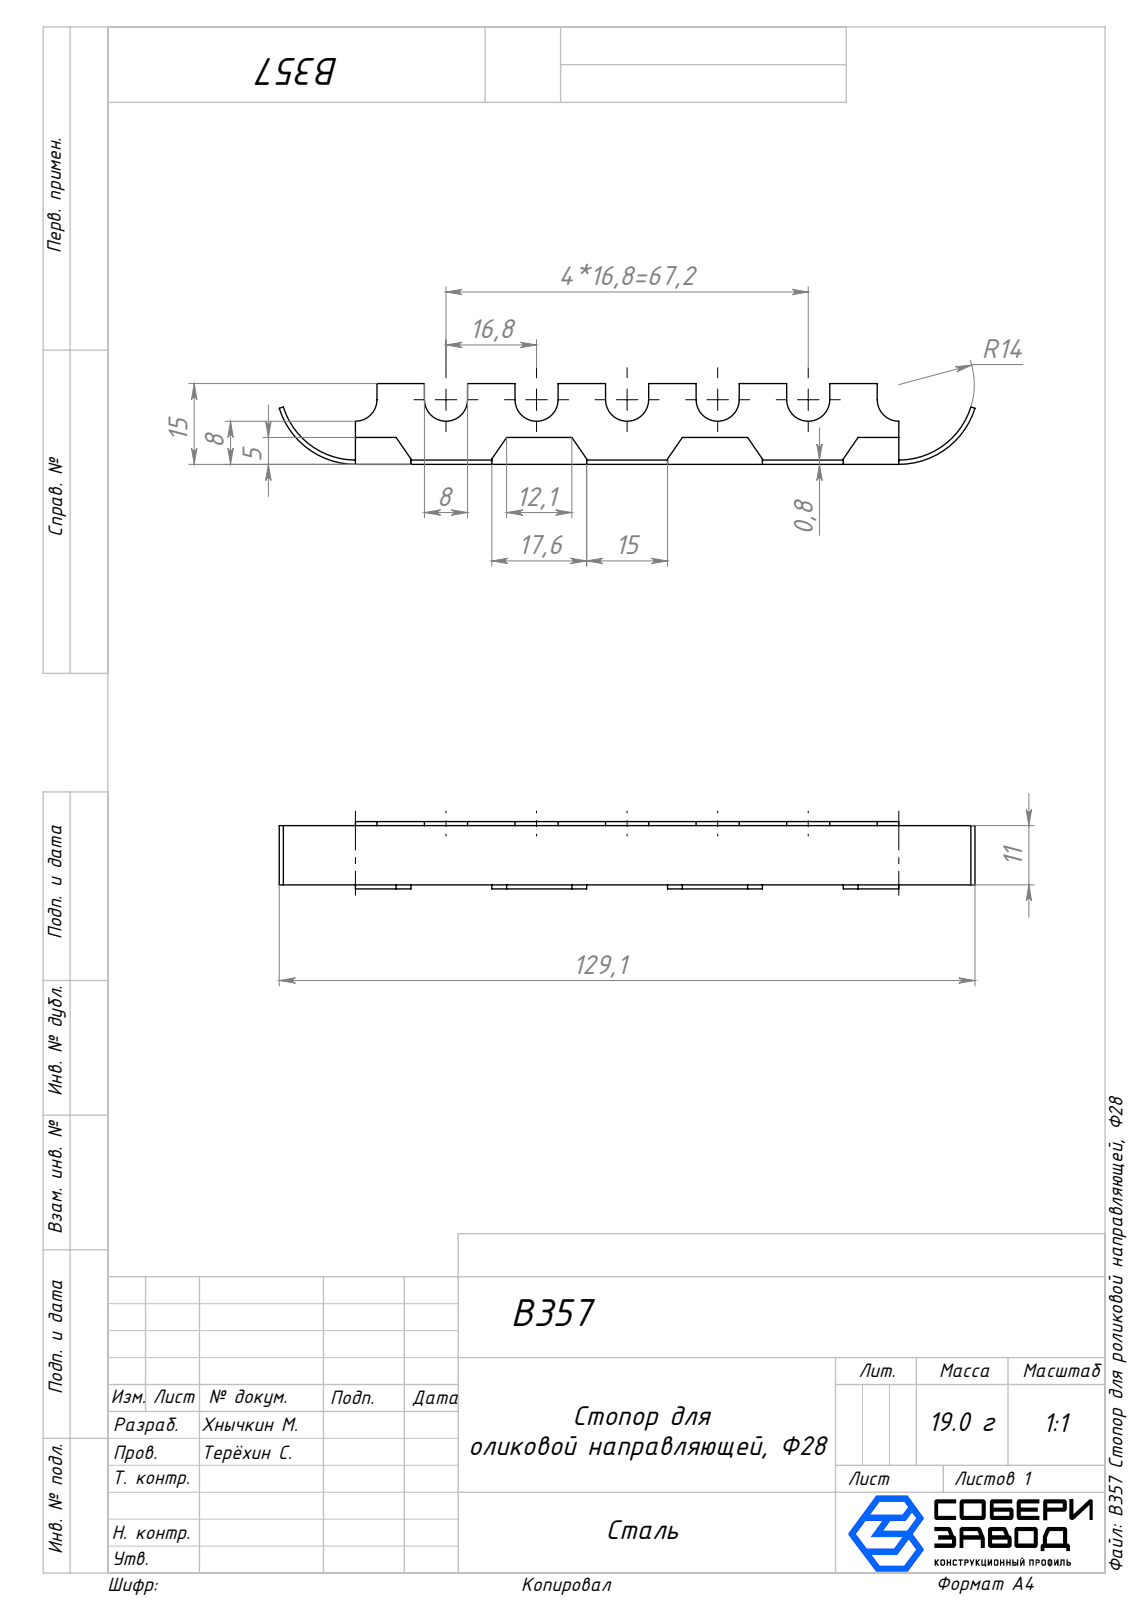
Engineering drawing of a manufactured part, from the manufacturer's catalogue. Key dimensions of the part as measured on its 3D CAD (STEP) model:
Part name (STEP PRODUCT): B357 Стопор для роликовой направляющей, Ф28
STEP written by: SolidWorks 2025 (AUTOMOTIVE_DESIGN)
Units: millimetres
Bodies: 1 solid, 75 faces (59 planar, 16 cylindrical, 0 other)
Overall size (bounding box): 129.07 × 15 × 12.5
Volume: 2 294 mm³ · Surface area: 6 210 mm²
Partial cylindrical surfaces — rounded edges, fillets, slot ends (radius × count): R4 ×7, R0.6 ×2, R14 ×2, R14.8 ×2
Main face-to-face distances: 0.75, 0.8, 11.75, 11, 12.5, 15, 14.2, 5, 4.2, 10
